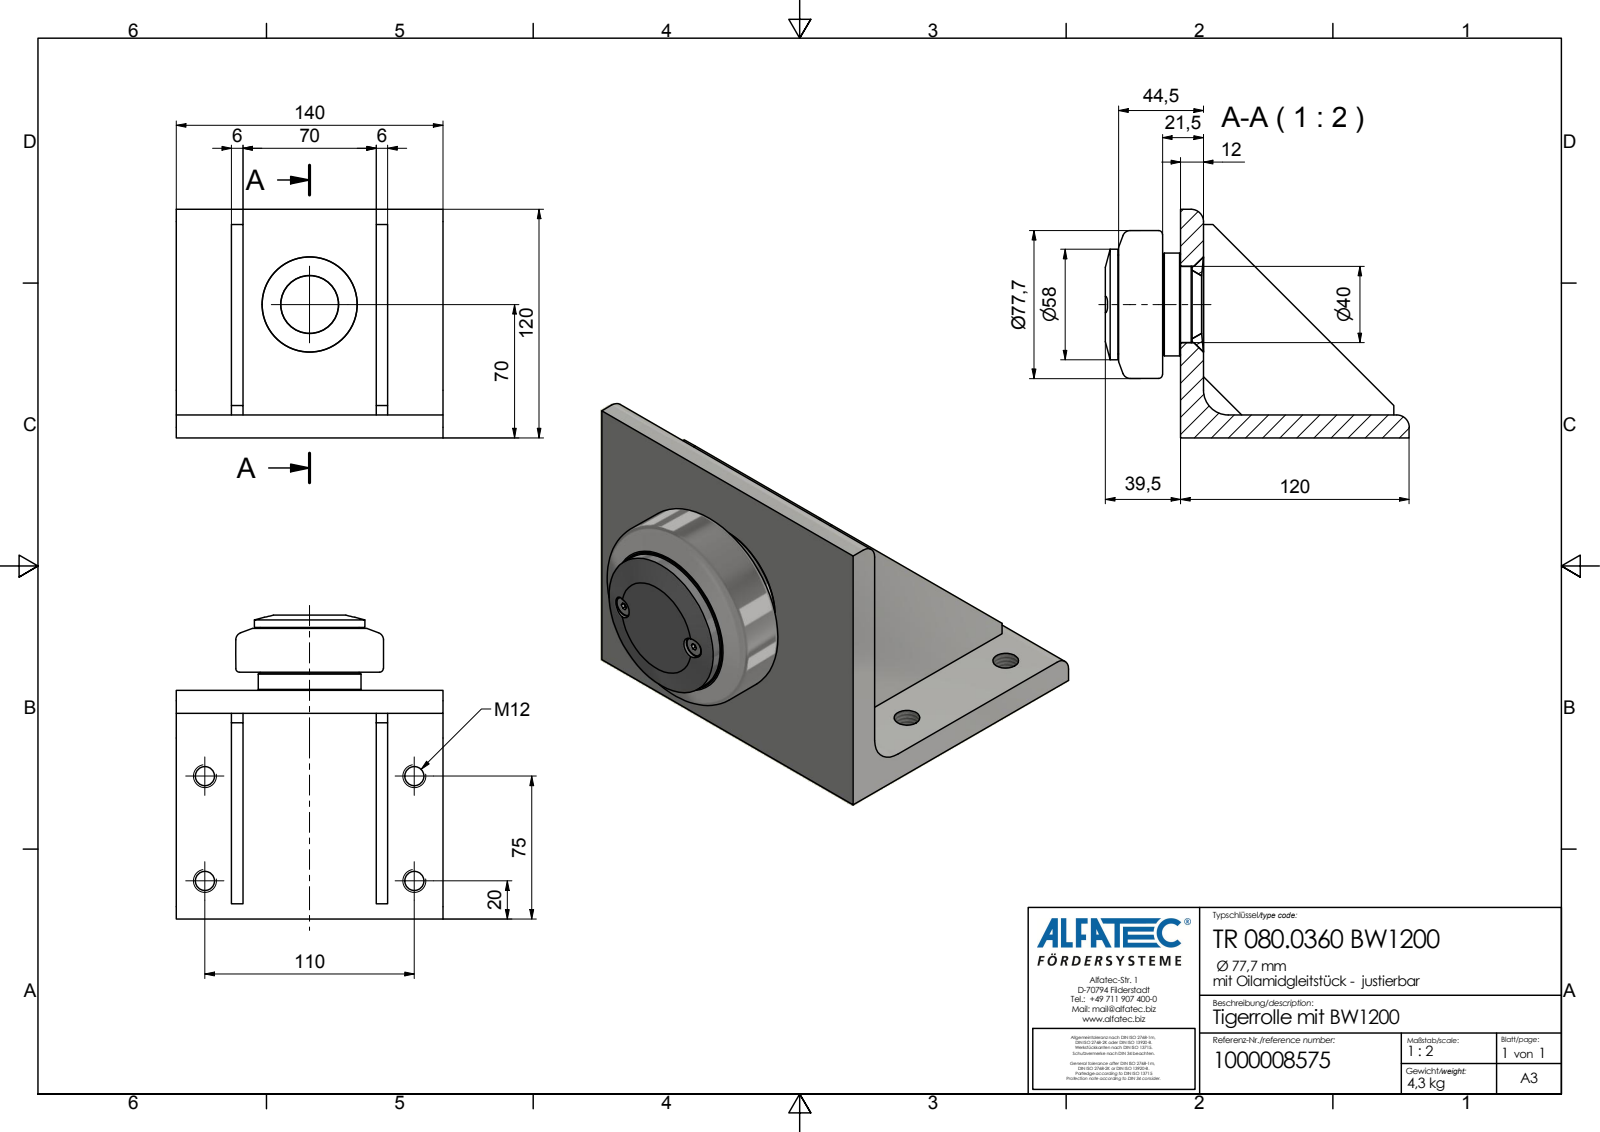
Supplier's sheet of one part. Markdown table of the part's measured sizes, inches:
| quantity | value |
| --- | --- |
| part name | TR 080.0360 BW1200_Kontur |
| STEP written by | Autodesk Inventor 2020 (AP242_MANAGED_MODEL_BASED_3D_ENGINEERING_MIM_LF) |
| units | inches |
| bodies | 1 solid, 67 faces (42 planar, 15 cylindrical, 10 other) |
| overall size | 6.28 × 5.512 × 4.724 |
| volume | 35.81 in³ |
| surface area | 165.5 in² |
| round holes (diameter × count) | 0.398 × 4, 0.339 × 2 |
| round bosses / shafts (diameter × count) | 0.307 × 2, 2.283 × 1, 2.126 × 1, 2.047 × 1 |
| partial cylindrical surfaces (radius × count) | 0.256 × 2, 0.512 × 1 |
| main face-to-face distances | 0.472, 2.992, 0.236, 1.142, 1.378, 4.134, 4.37, 3.228, 2.756, 5.512 |
| hole center spacings | 2.165, 4.331, 4.842, 1.535 |
